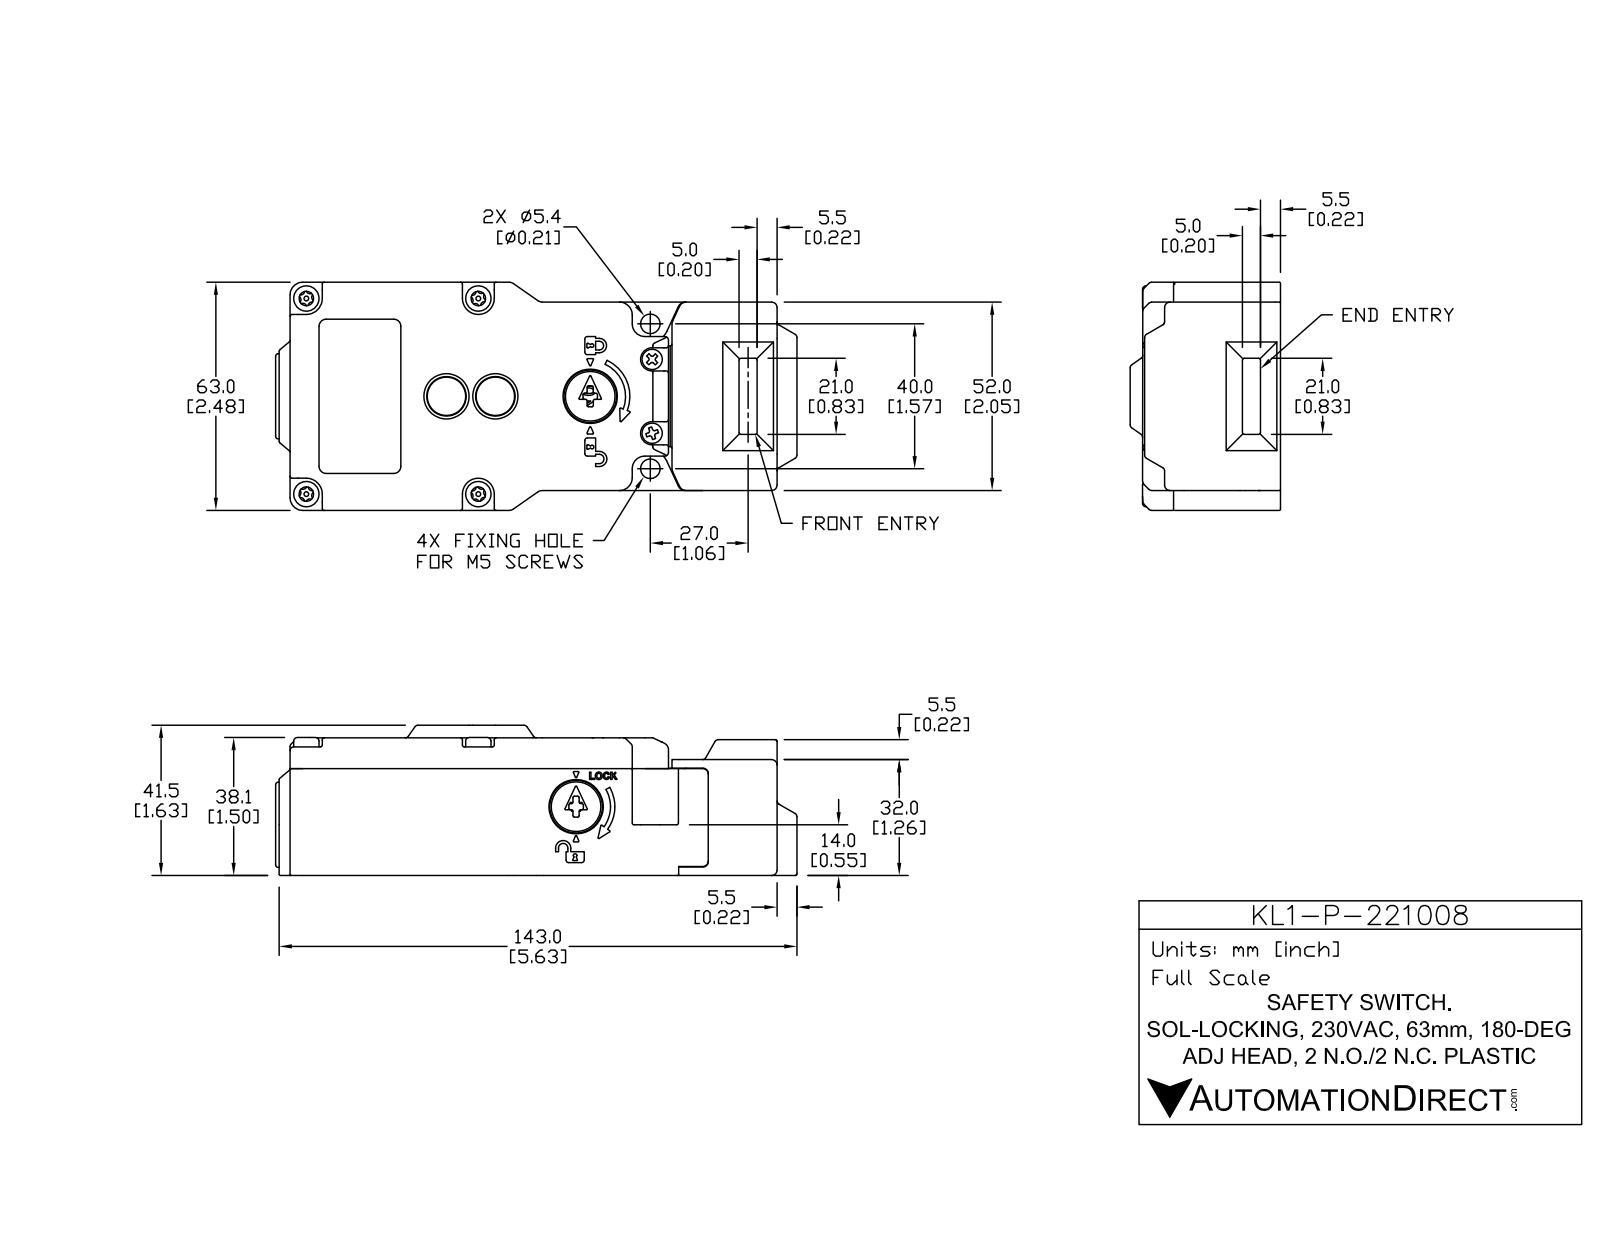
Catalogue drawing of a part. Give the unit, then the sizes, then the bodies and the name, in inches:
Units: inches
Overall size (bounding box): 5.669 × 2.48 × 1.634
Round holes (diameter × count): ⌀0.102 ×4, ⌀0.134 ×4, ⌀0.157 ×4, ⌀0.161 ×4, ⌀0.177 ×4, ⌀0.197 ×4, ⌀0.079 ×2, ⌀0.083 ×2, ⌀0.118 ×2, ⌀0.126 ×2, ⌀0.142 ×2, ⌀0.264 ×2
Round bosses / shafts (diameter × count): ⌀0.276 ×4, ⌀0.138 ×4, ⌀0.051 ×4, ⌀0.197 ×3, ⌀0.039 ×3, ⌀0.571 ×2, ⌀0.417 ×2, ⌀0.362 ×2
Partial cylindrical surfaces — rounded edges, fillets, slot ends (radius × count): R0.02 ×348, R0.012 ×126, R0.039 ×106, R0.008 ×30, R0.016 ×24, R0.059 ×16, R0.006 ×14, R0.028 ×12
Main face-to-face distances: 0.098, 0.118, 0.217, 1.496, 1.398, 1.402, 1.303, 0.094, 2.264, 2.146
Hole centre spacings: 0.404, 0.498, 0.515, 0.549, 0.784, 0.803, 1.079, 1.118
Volume: 6.348 in³ · Surface area: 118.8 in²
Bodies: 18 solids, 3047 faces (909 planar, 1225 cylindrical, 913 other)
Part name (STEP PRODUCT): KL1-P-221008
STEP written by: SolidWorks 2017 (AUTOMOTIVE_DESIGN)
